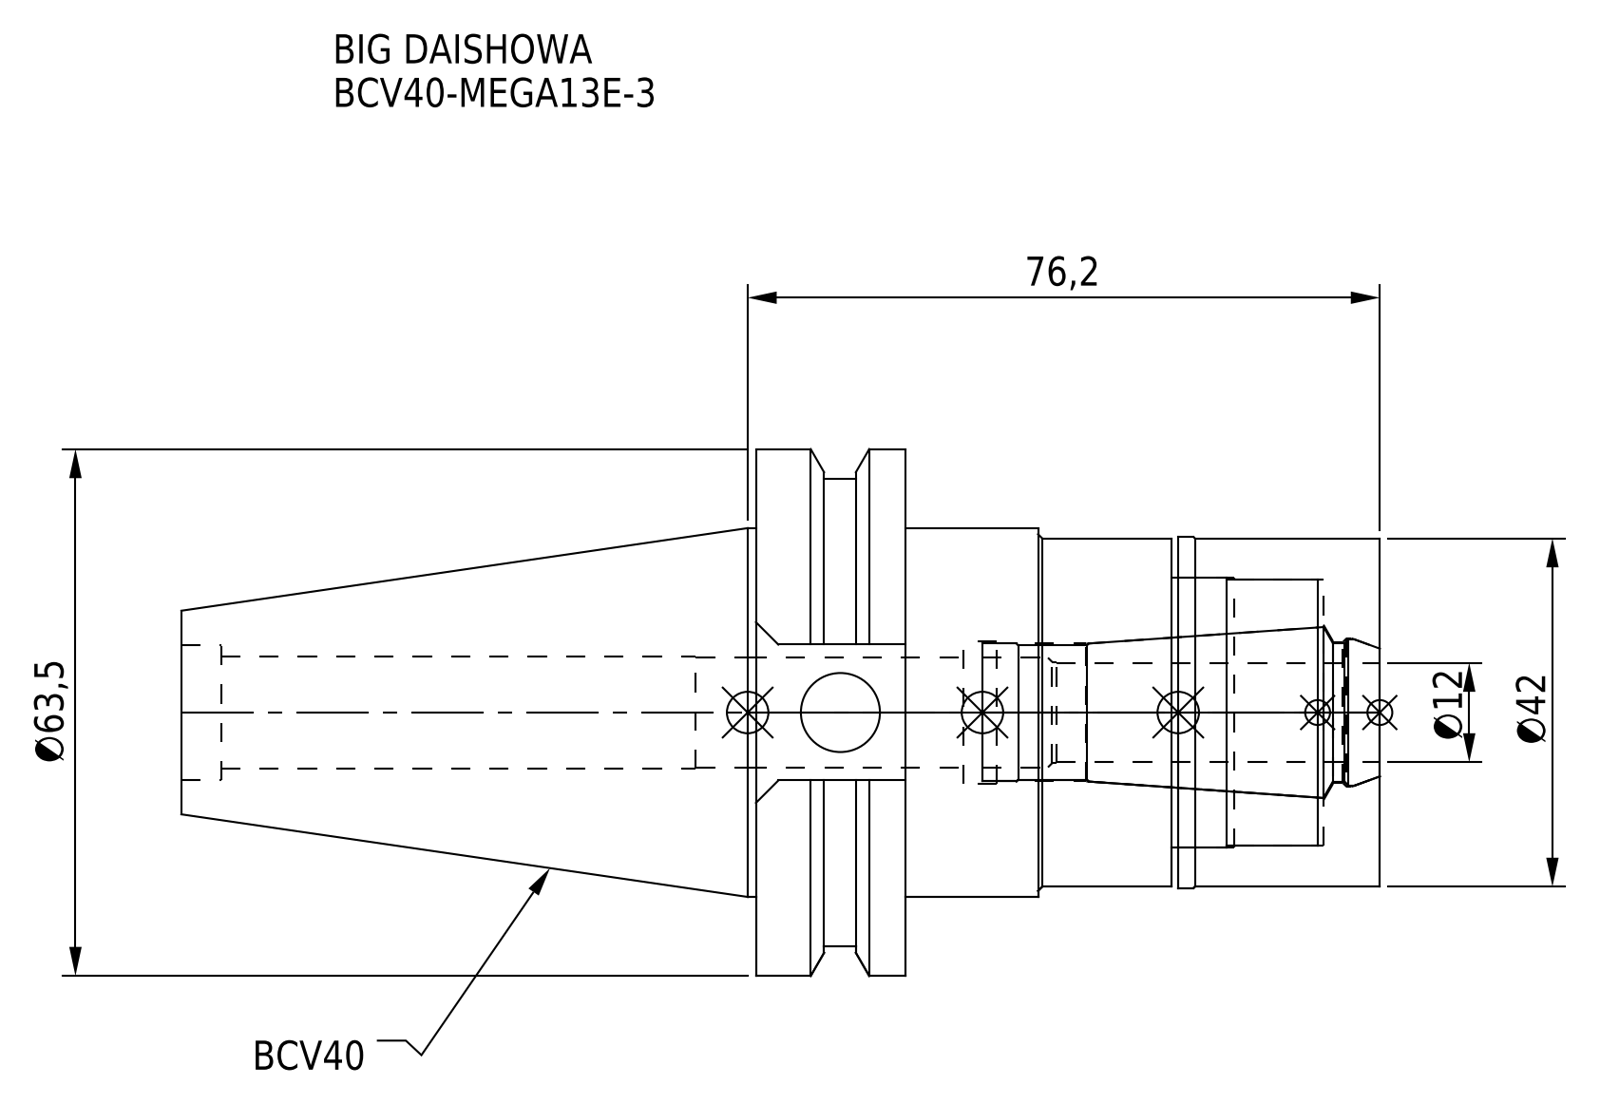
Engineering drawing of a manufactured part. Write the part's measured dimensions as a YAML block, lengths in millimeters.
part_name: "BCV40-MEGA13E-3-120-FreeParts; BCV40-MEGA13E-3_1.stp; BCV40-MEGA13E-3-120.stp; MEN13_1.stp (+3 more)"
step_written_by: "SolidWorks 2019 (CONFIG_CONTROL_DESIGN)"
units: millimeters
bodies: {solids: 2, faces: 90, planar: 30, cylindrical: 42, other: 18}
overall_size: [144.45, 63.5, 61.35]
volume: 171424
surface_area: 36857
round_holes:
  - {diameter: 9.53, count: 1}
  - {diameter: 13.3, count: 1}
  - {diameter: 13.6, count: 1}
  - {diameter: 16.32, count: 1}
  - {diameter: 16.6, count: 1}
  - {diameter: 17, count: 1}
  - {diameter: 17.2, count: 1}
  - {diameter: 17.9, count: 1}
  - {diameter: 32, count: 1}
  - {diameter: 32.5, count: 1}
round_bosses_or_shafts:
  - {diameter: 63.5, count: 1}
  - {diameter: 56.36, count: 1}
  - {diameter: 44.45, count: 1}
  - {diameter: 42.3, count: 1}
  - {diameter: 42, count: 1}
face_to_face_distances: [18.05, 57.15, 75.2, 25.1, 24.3, 32.85, 50.9, 0.8, 32.05, 50.1]
